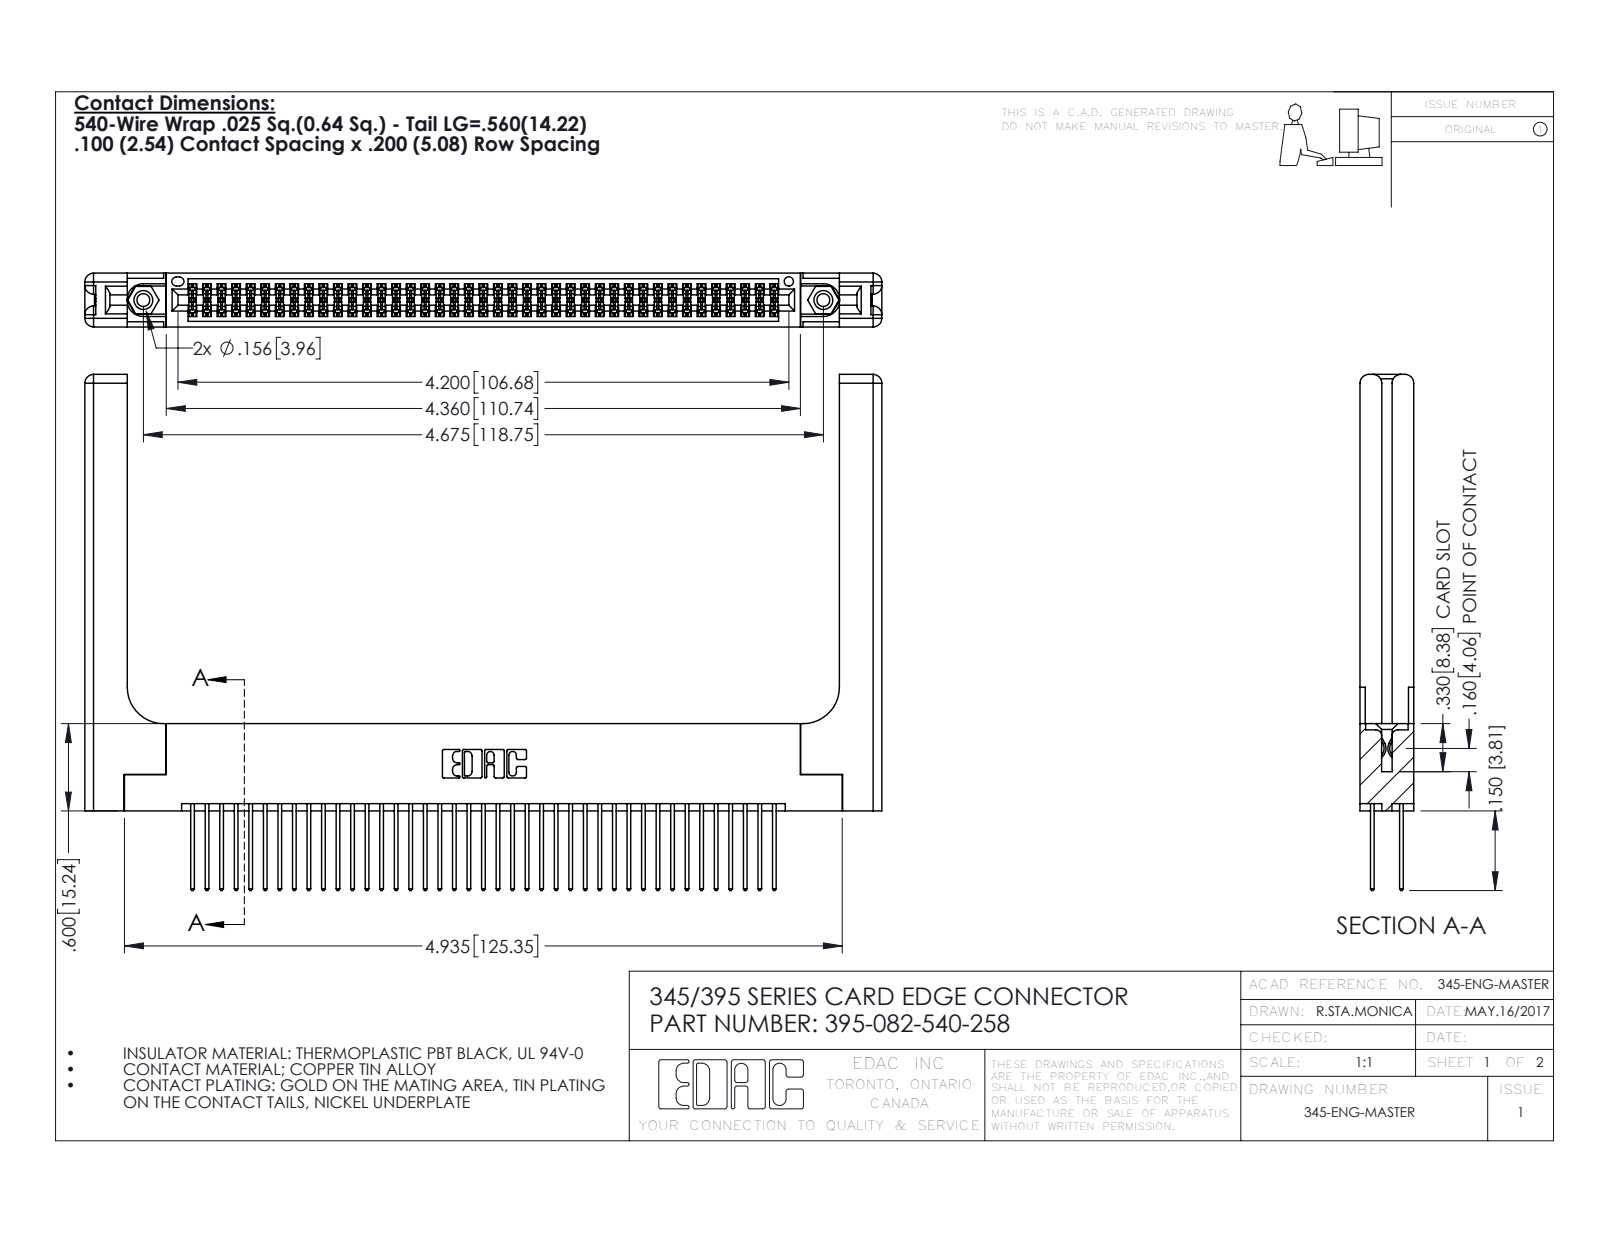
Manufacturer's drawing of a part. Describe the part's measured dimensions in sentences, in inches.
The part is named "345 Part_Flush Mounting Lugs - 0.156 Dia-TH; 345-220-058_345-220-058; 395-082-540-258; 345-250-001_345-250-001-102 (+1 more)". Its 3-D file was written by "SolidWorks 2016 (CONFIG_CONTROL_DESIGN)". It is 87 solids with 4482 faces: 2934 planar, 1488 cylindrical and 60 other. Overall it measures 5.479 by 3.547 by 0.37 inches. Its volume is 1.361 cubic inches and its surface area 41.71 square inches. Round holes: 2 of diameter 0.089, 2 of diameter 0.125, 2 of diameter 0.156, 1 of diameter 0.064. Round bosses or shafts: 2 of diameter 0.155. Partial cylindrical surfaces (rounded edges, fillets, slot ends): 123 of radius 0.006, 82 of radius 0.01, 22 of radius 0.01, 16 of radius 0.06, 6 of radius 0.007, 6 of radius 0.031, 3 of radius 0.026, 2 of radius 0.014. The main face-to-face distances are 0.072, 0.298, 0.37, 0.2, 0.098, 0.272, 0.025, 0.225, 0.175, 0.148. The hole center spacings are 0.27, 4.439, 4.675.
